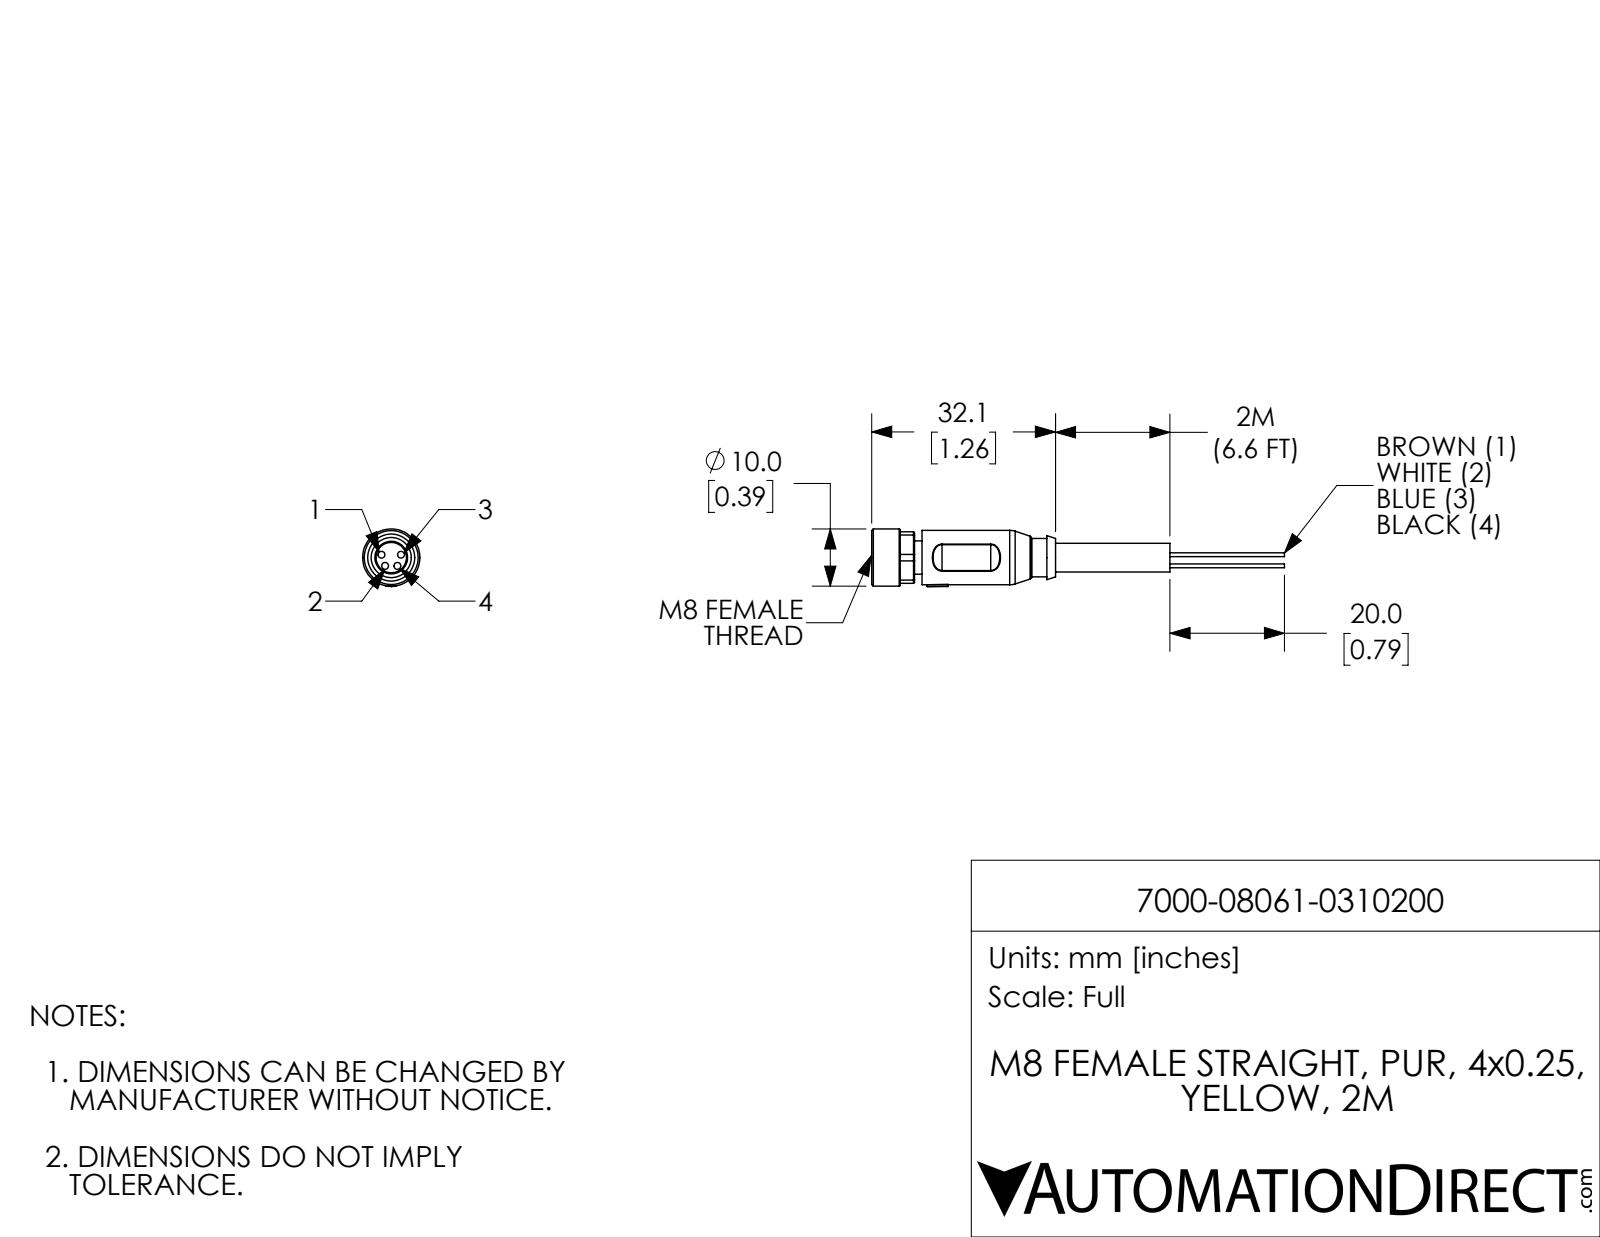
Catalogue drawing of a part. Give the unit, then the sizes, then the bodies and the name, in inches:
Units: inches
Overall size (bounding box): 2.839 × 0.396 × 0.394
Round holes (diameter × count): ⌀0.047 ×4, ⌀0.276 ×1
Round bosses / shafts (diameter × count): ⌀0.026 ×4, ⌀0.394 ×1, ⌀0.374 ×1, ⌀0.264 ×1, ⌀0.228 ×1, ⌀0.224 ×1, ⌀0.197 ×1
Partial cylindrical surfaces — rounded edges, fillets, slot ends (radius × count): R0.008 ×4, R0.098 ×4, R0.193 ×1, R0.199 ×1
Main face-to-face distances: 0.327, 0.051, 0.969, 0.354, 0.059, 0.028, 1.756, 1.705, 0.268, 0.319
Hole centre spacings: 0.07, 0.071, 0.081, 0.133, 0.084, 0.134
Volume: 0.141 in³ · Surface area: 2.944 in²
Bodies: 1 solid, 115 faces (38 planar, 46 cylindrical, 31 other)
Part name (STEP PRODUCT): 7000-08061-0310200
STEP written by: SolidWorks 2021 (CONFIG_CONTROL_DESIGN)
